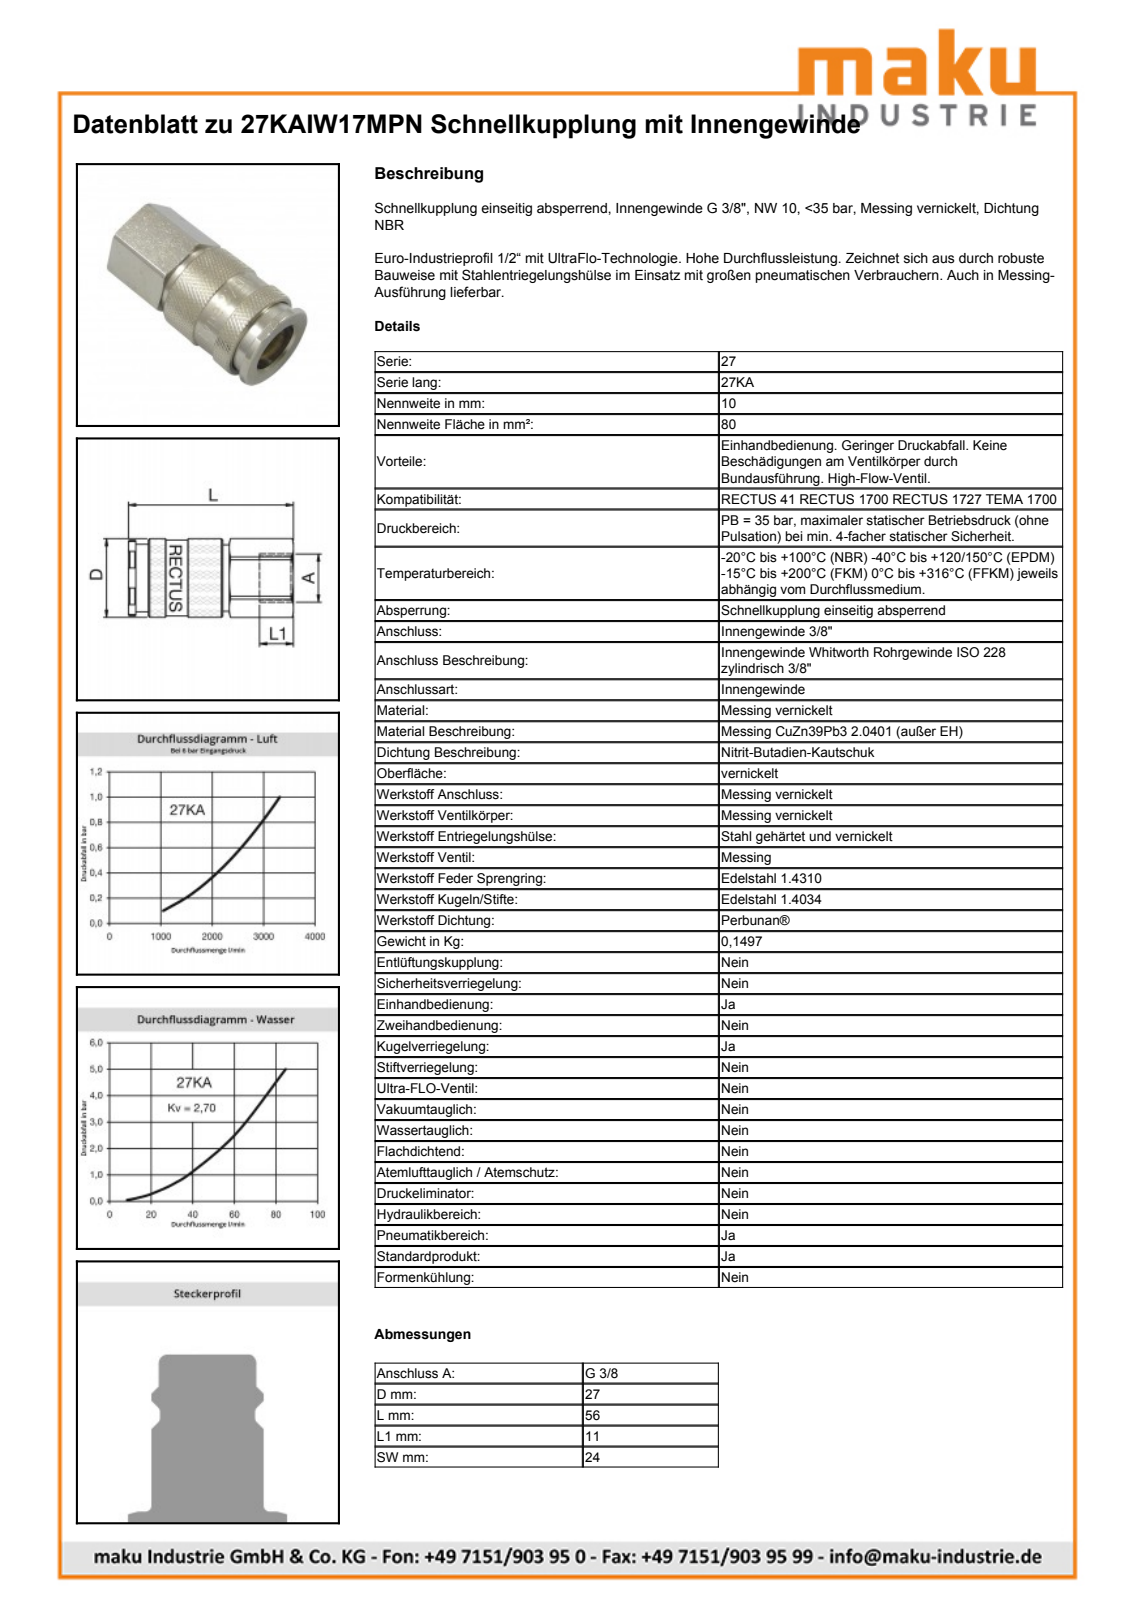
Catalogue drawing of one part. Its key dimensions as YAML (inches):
part_name: "D106032"
step_written_by: "Autodesk Inventor 2011 (AUTOMOTIVE_DESIGN)"
units: inches
bodies: {solids: 2, faces: 743, planar: 320, cylindrical: 84, other: 339}
overall_size: [2.262, 1.069, 1.069]
volume: 1.57
surface_area: 16.48
round_holes:
  - {diameter: 0.589, count: 1}
  - {diameter: 0.799, count: 1}
  - {diameter: 0.825, count: 1}
  - {diameter: 0.919, count: 1}
  - {diameter: 0.927, count: 1}
round_bosses_or_shafts:
  - {diameter: 1.069, count: 1}
  - {diameter: 1.024, count: 1}
  - {diameter: 0.909, count: 1}
  - {diameter: 0.896, count: 1}
  - {diameter: 0.787, count: 1}
partial_cylinders:
  - {radius: 0.386, count: 1}
  - {radius: 0.508, count: 1}
  - {radius: 0.533, count: 1}
face_to_face_distances: [0.945, 2.262, 1.798, 0.463, 0.248, 1.55, 2.014, 1.252, 1.004, 0.546]
